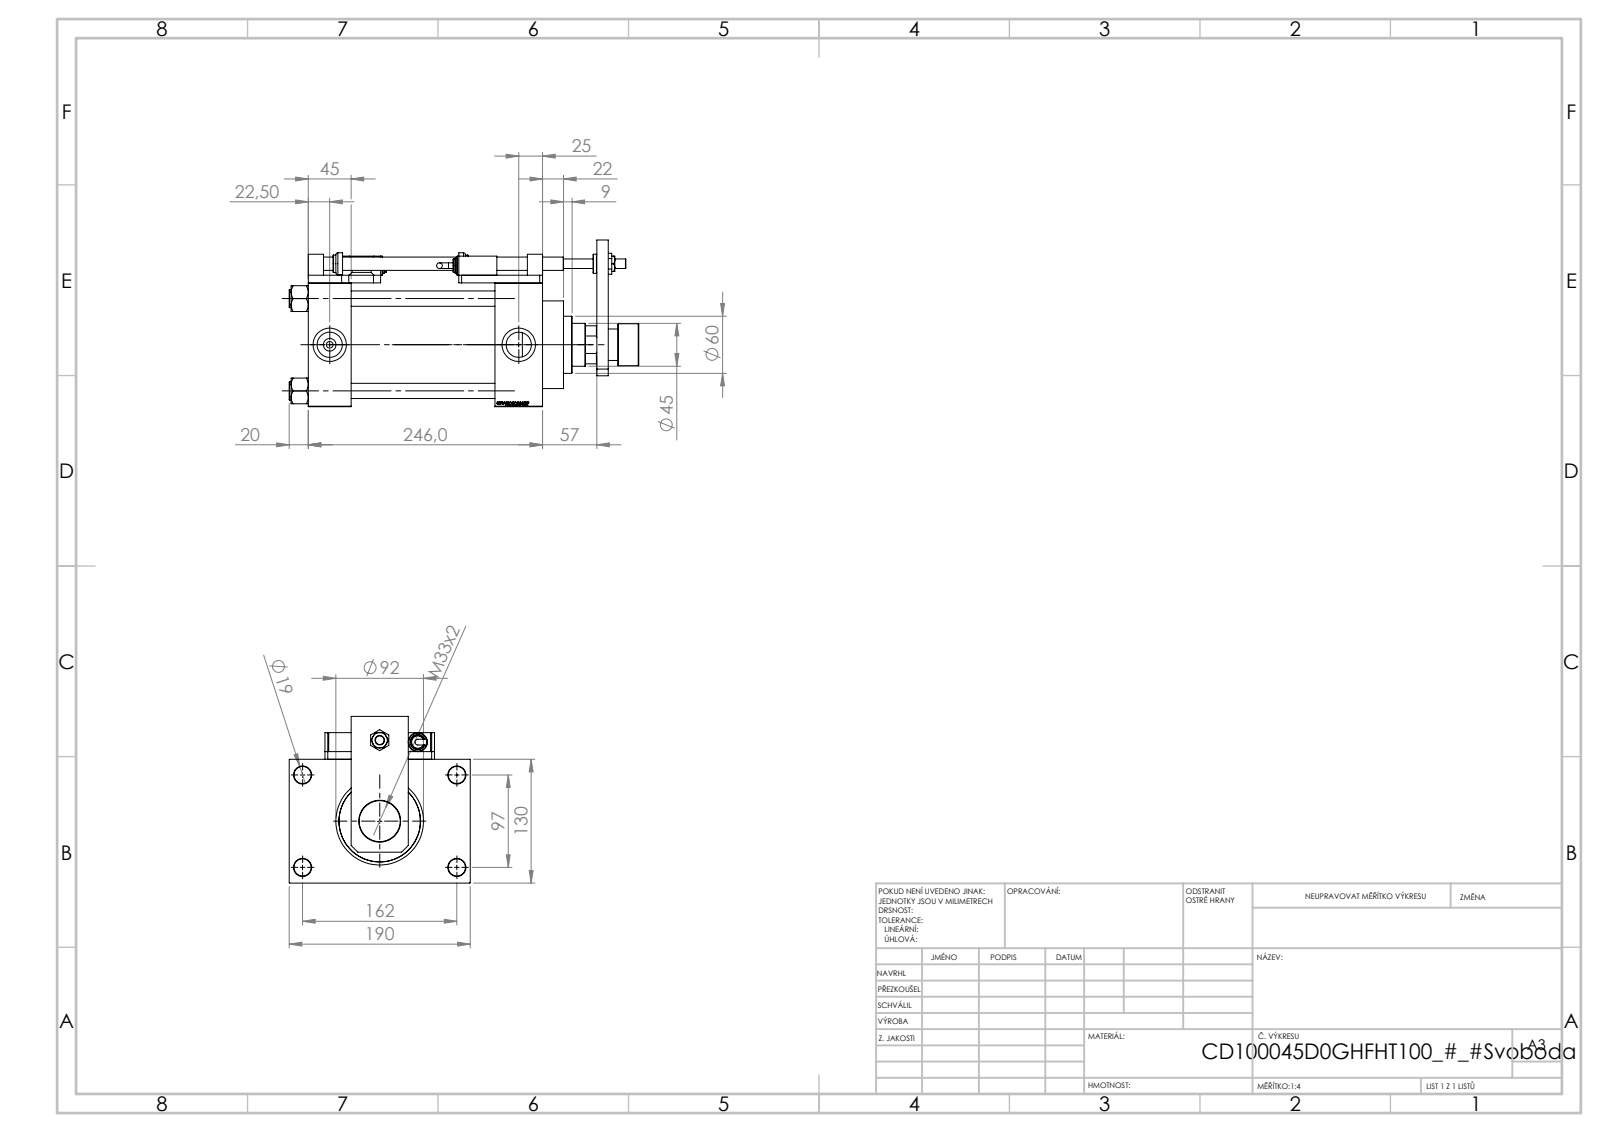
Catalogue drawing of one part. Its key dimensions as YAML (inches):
part_name: "V215CD_SWITCH_Q_BLOK; V215CD_NUT_M5_D; V215CD_SWITCH_Q_NUT10; V215CD_SWITCH_Q_PODLOZKA_BACK (+8 more)"
step_written_by: "SolidWorks 2019 (CONFIG_CONTROL_DESIGN)"
units: inches
bodies: {solids: 25, faces: 1392, planar: 669, cylindrical: 160, other: 563}
overall_size: [14.449, 7.48, 6.89]
volume: 198.5
surface_area: 841.9
round_holes:
  - {diameter: 0.335, count: 4}
  - {diameter: 0.531, count: 4}
  - {diameter: 0.63, count: 4}
  - {diameter: 0.709, count: 4}
  - {diameter: 0.276, count: 2}
  - {diameter: 1.041, count: 2}
  - {diameter: 1.378, count: 2}
  - {diameter: 0.394, count: 1}
  - {diameter: 0.551, count: 1}
  - {diameter: 1.24, count: 1}
  - {diameter: 1.299, count: 1}
  - {diameter: 1.772, count: 1}
round_bosses_or_shafts:
  - {diameter: 0.748, count: 4}
  - {diameter: 0.787, count: 3}
  - {diameter: 0.63, count: 2}
  - {diameter: 0.551, count: 2}
  - {diameter: 0.236, count: 2}
  - {diameter: 4.173, count: 1}
  - {diameter: 3.622, count: 1}
  - {diameter: 2.362, count: 1}
partial_cylinders:
  - {radius: 0.295, count: 4}
face_to_face_distances: [1.772, 5.118, 7.913, 9.685, 5.945, 0.315, 1.969, 7.717, 5.433, 6.299]
hole_center_spacings: [1.281, 2.698, 3.717, 3.815, 4.026, 5.096, 6.367, 1.26]
